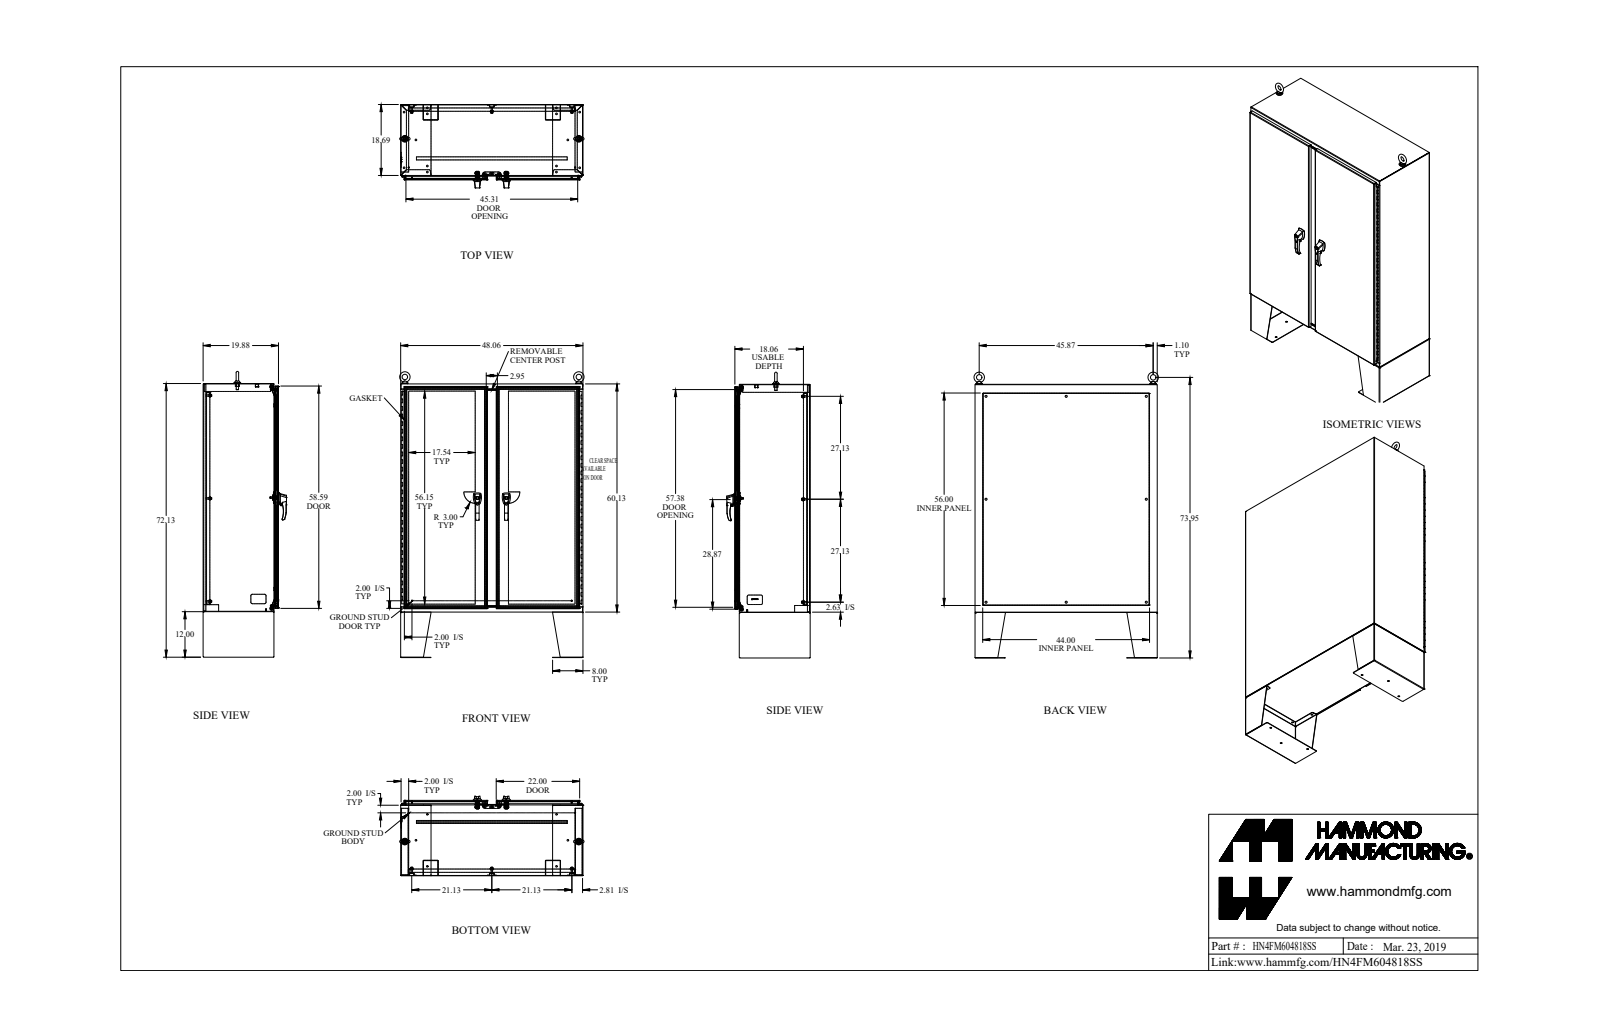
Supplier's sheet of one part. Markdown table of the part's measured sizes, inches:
| quantity | value |
| --- | --- |
| part name | HN4FM604818SS |
| STEP written by | SolidWorks 2018 (AUTOMOTIVE_DESIGN) |
| units | inches |
| bodies | 130 solids, 3760 faces (1740 planar, 1659 cylindrical, 361 other) |
| overall size | 75.321 × 48.606 × 21.99 |
| volume | 1 640 in³ |
| surface area | 33 031 in² |
| round holes (diameter × count) | 0.304 × 20, 0.437 × 14, 0.307 × 8, 0.35 × 8, 0.563 × 8, 0.25 × 7, 0.445 × 7, 0.281 × 4, 0.313 × 4, 0.39 × 4, 0.201 × 3, 0.257 × 3 |
| round bosses / shafts (diameter × count) | 1 × 11, 0.65 × 8, 0.375 × 8, 0.332 × 8, 0.75 × 4, 0.625 × 4, 0.44 × 4, 0.37 × 4 |
| partial cylindrical surfaces (radius × count) | 0.125 × 40, 0.5 × 34, 0.018 × 32, 0.06 × 31, 0.048 × 29, 0.143 × 29, 0.318 × 14, 0.03 × 12 |
| main face-to-face distances | 0.095, 47.967, 19.78, 19.778, 0.125, 1.782, 1.687, 1.657, 1.562, 60.03 |
| hole center spacings | 6, 12, 18, 24, 30, 46.593, 1.61, 6.144 |
